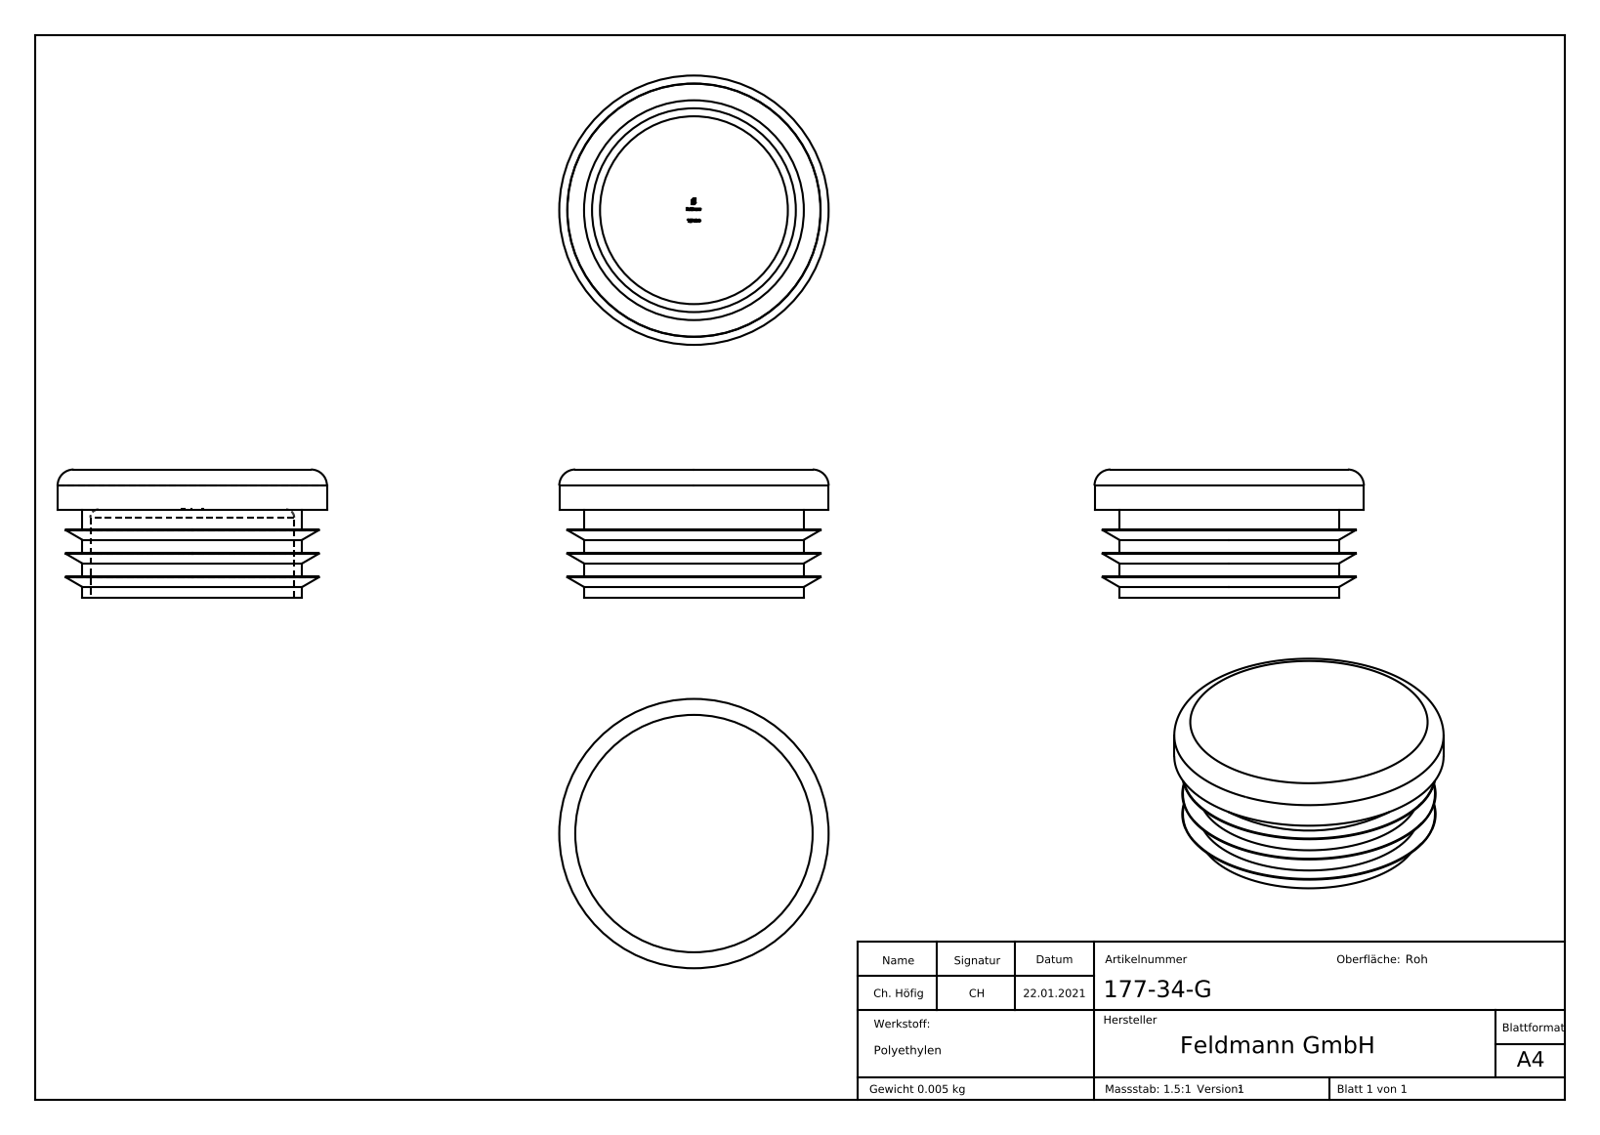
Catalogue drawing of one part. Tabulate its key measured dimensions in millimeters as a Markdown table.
| quantity | value |
| --- | --- |
| part name | 177-34-G |
| STEP written by | SolidWorks 2018 (CONFIG_CONTROL_DESIGN) |
| units | millimeters |
| bodies | 1 solid, 267 faces (148 planar, 12 cylindrical, 107 other) |
| overall size | 33.7 × 33.7 × 16 |
| volume | 5 699 mm³ |
| surface area | 4 962 mm² |
| round holes (diameter × count) | 25.5 × 1 |
| round bosses / shafts (diameter × count) | 33.7 × 1, 27.5 × 1 |
| main face-to-face distances | 5, 2.95, 5.45, 10.45, 5.9, 8.4, 13.4, 2.5, 7.5, 2.6 |
